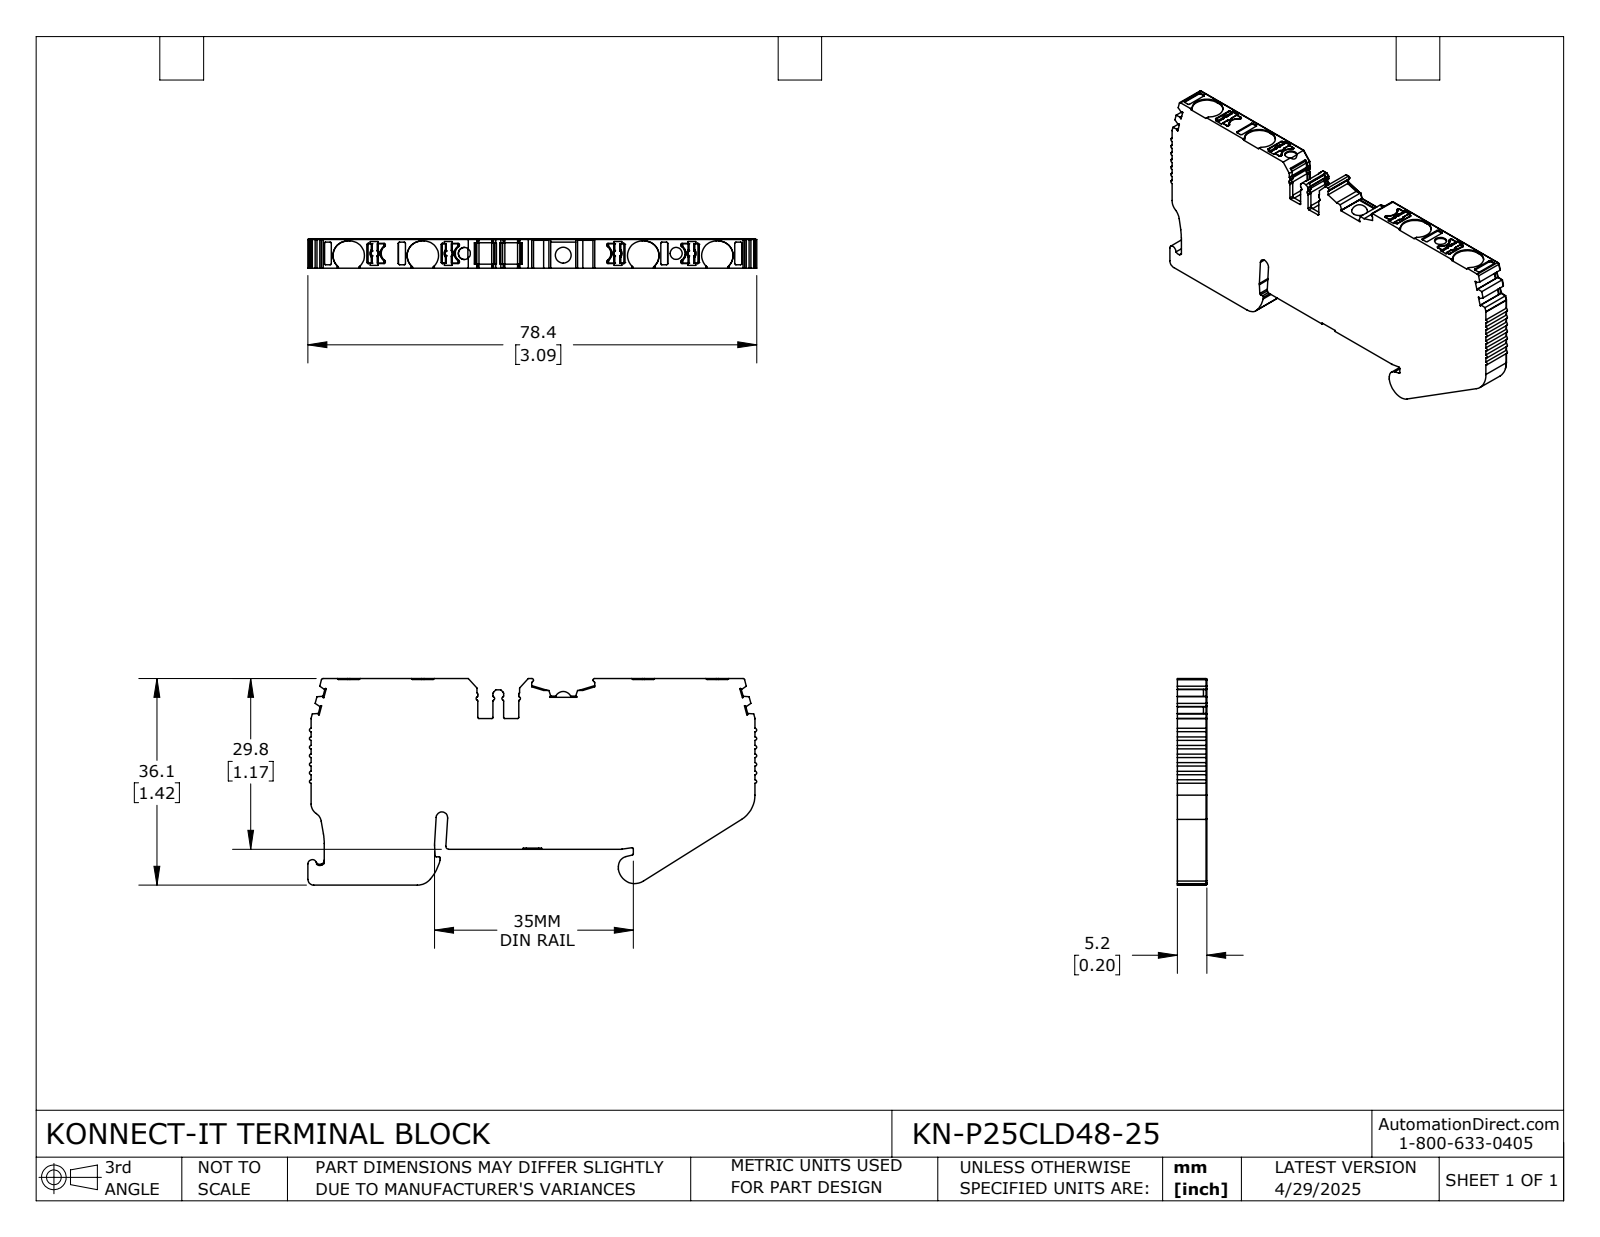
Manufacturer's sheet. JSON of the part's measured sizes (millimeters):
{"part_name": "KN-P25CLD48-25", "step_written_by": "SolidWorks 2024 (CONFIG_CONTROL_DESIGN)", "units": "millimeters", "bodies": {"solids": 1, "faces": 740, "planar": 381, "cylindrical": 291, "other": 68}, "overall_size": [78.36, 36.07, 5.15], "volume_mm3": 11975, "surface_area_mm2": 6221, "round_holes": [[2.1, 2]], "partial_cylinders_radius": [[0.2, 78], [0.3, 39], [0.1, 21], [0.5, 18], [0.15, 16], [0.4, 9], [2.55, 8], [1.5, 4]], "face_to_face_distances": [5.15, 29.61, 29.81, 6.26, 35.87, 36.07, 77.52, 1.2, 5, 4.5], "hole_center_spacings": [36.98]}
